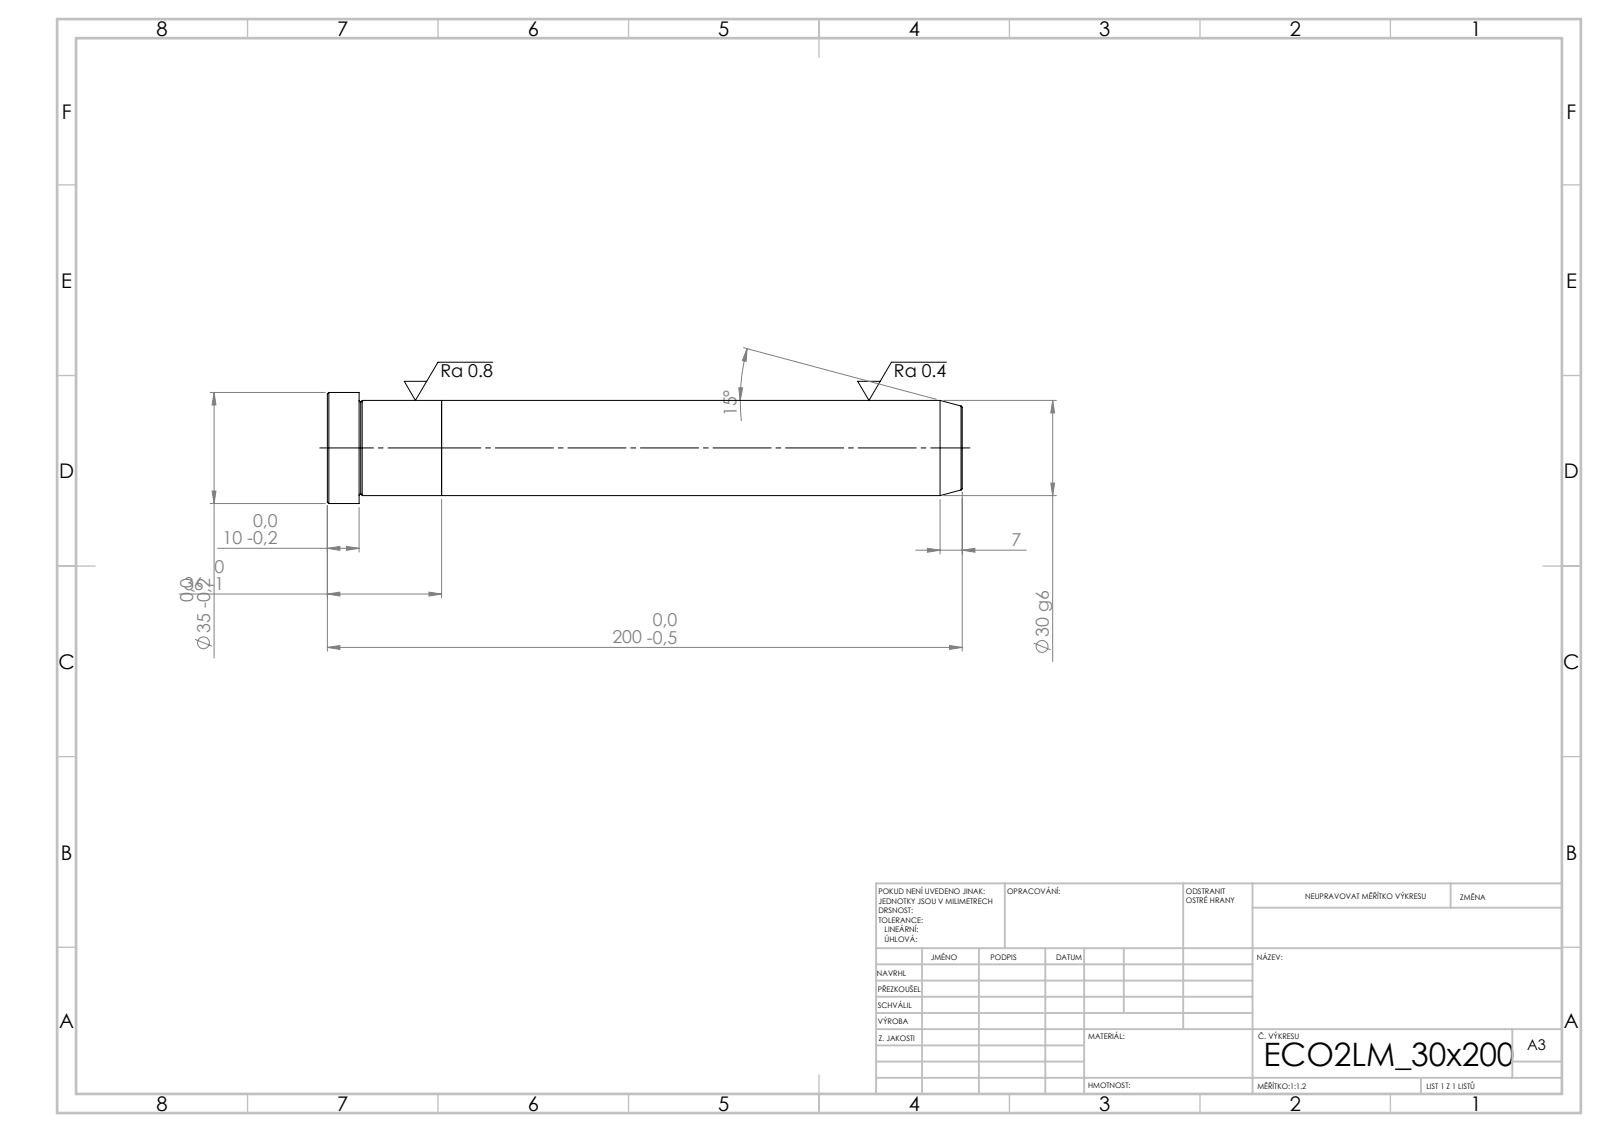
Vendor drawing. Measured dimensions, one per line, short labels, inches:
written by: SolidWorks 2019 (CONFIG_CONTROL_DESIGN)
unit: in
bodies: 2 solids, 21 faces (5 planar, 6 cylindrical, 10 other)
size: 7.874 × 1.378 × 1.378
volume: 8.743 in³; area: 34.36 in²
bosses: 1× ⌀1.378, 1× ⌀1.181
face distances: 1.417, 6.457, 7.874, 7.48, 1.024, 0.394
